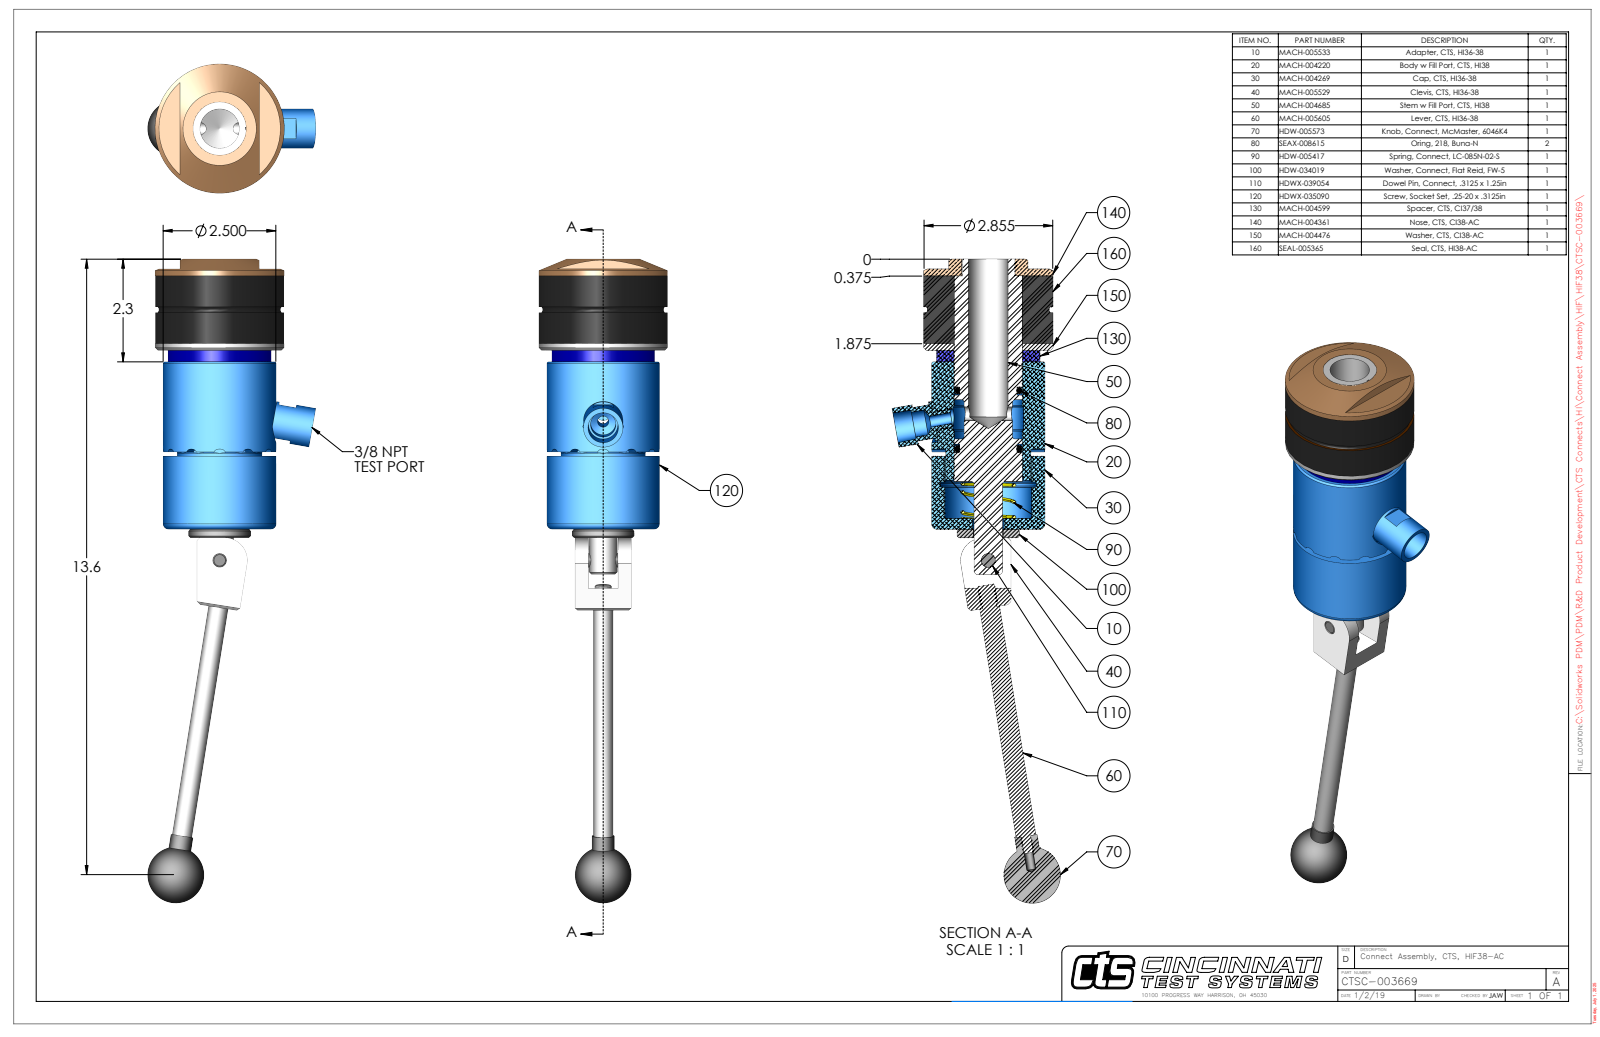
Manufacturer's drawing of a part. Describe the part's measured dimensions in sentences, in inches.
The part is named "CTSC-003669". Its 3-D file was written by "SolidWorks 2023 (AUTOMOTIVE_DESIGN)". It is 10 solids with 309 faces: 110 planar, 126 cylindrical and 73 other. Overall it measures 14.275 by 3.716 by 2.855 inches. Its volume is 32.86 cubic inches and its surface area 163 square inches. Round holes: 2 of diameter 0.201, 1 of diameter 0.15, 1 of diameter 0.25, 1 of diameter 0.311, 1 of diameter 0.312, 1 of diameter 0.313, 1 of diameter 0.314, 1 of diameter 0.562, 1 of diameter 0.656, 1 of diameter 0.696, 1 of diameter 0.875, 1 of diameter 1.172. Round bosses or shafts: 1 of diameter 2.855, 1 of diameter 2.855, 1 of diameter 2.5, 1 of diameter 2.281, 1 of diameter 1.875, 1 of diameter 1.5, 1 of diameter 1.498, 1 of diameter 1.38. Partial cylindrical surfaces (rounded edges, fillets, slot ends): 12 of radius 0.12, 2 of radius 0.029, 1 of radius 0.19, 1 of radius 0.195, 1 of radius 0.47, 1 of radius 0.471, 1 of radius 0.5, 1 of radius 1.192. The main face-to-face distances are 1.5, 0.152, 1.652, 0.25, 0.402, 1.902, 3.713, 3.963, 4.115, 5.615. The hole center spacings are 0.74, 2.118, 2.858.
